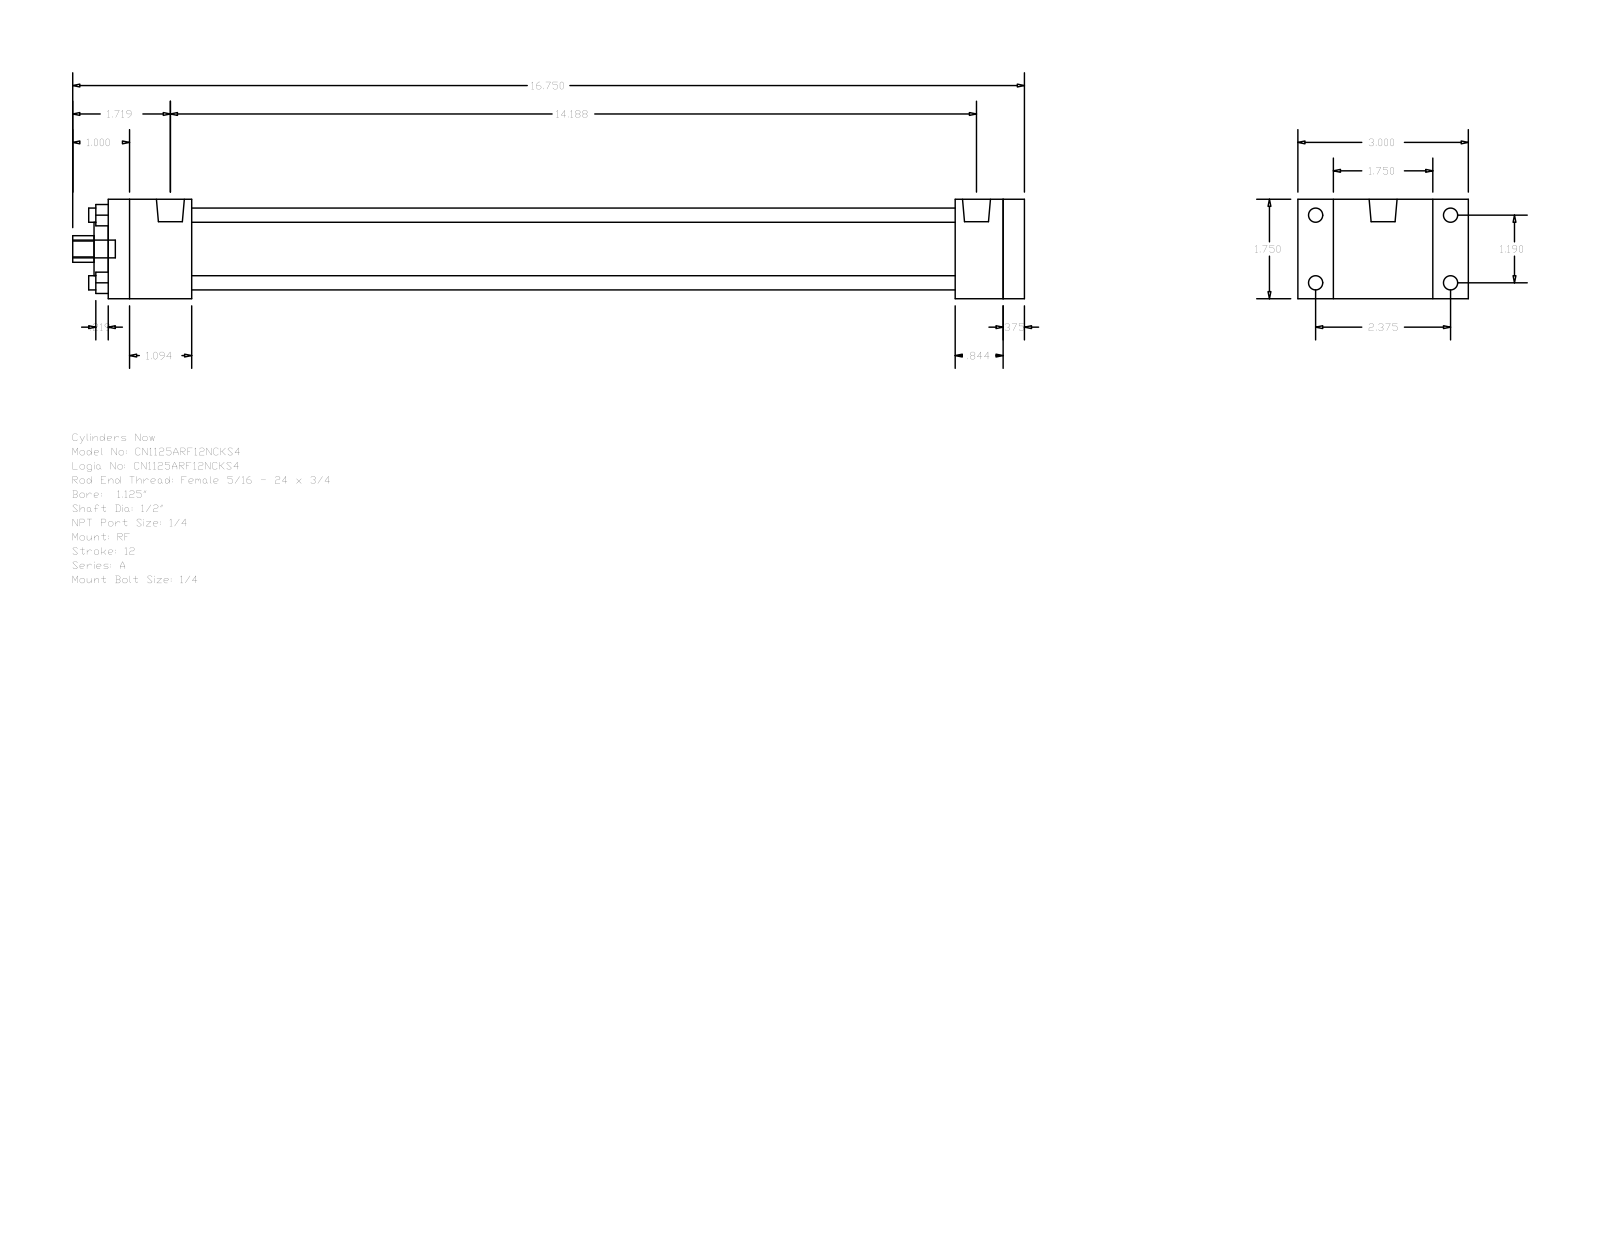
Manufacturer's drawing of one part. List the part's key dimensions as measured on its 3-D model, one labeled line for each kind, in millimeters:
Part name (STEP PRODUCT): A_RF__0112_0.5
STEP written by: GSSL Pune (CONFIG_CONTROL_DESIGN)
Units: millimetres
Bodies: 0 solids, 92 faces (64 planar, 28 cylindrical, 0 other)
Overall size (bounding box): 425.45 × 76.2 × 44.45
Round holes (diameter × count): ⌀6.35 ×4, ⌀12.7 ×1, ⌀23.81 ×1, ⌀31.88 ×1
Round bosses / shafts (diameter × count): ⌀6.35 ×4, ⌀5.56 ×4, ⌀12.49 ×2, ⌀7.94 ×1
Partial cylindrical surfaces — rounded edges, fillets, slot ends (radius × count): R5.94 ×1
Main face-to-face distances: 44.46, 9.52, 400.05, 409.57, 37.3, 378.61, 341.31, 362.75, 372.27, 21.44
Hole centre spacings: 21.37, 30.22, 42.74
